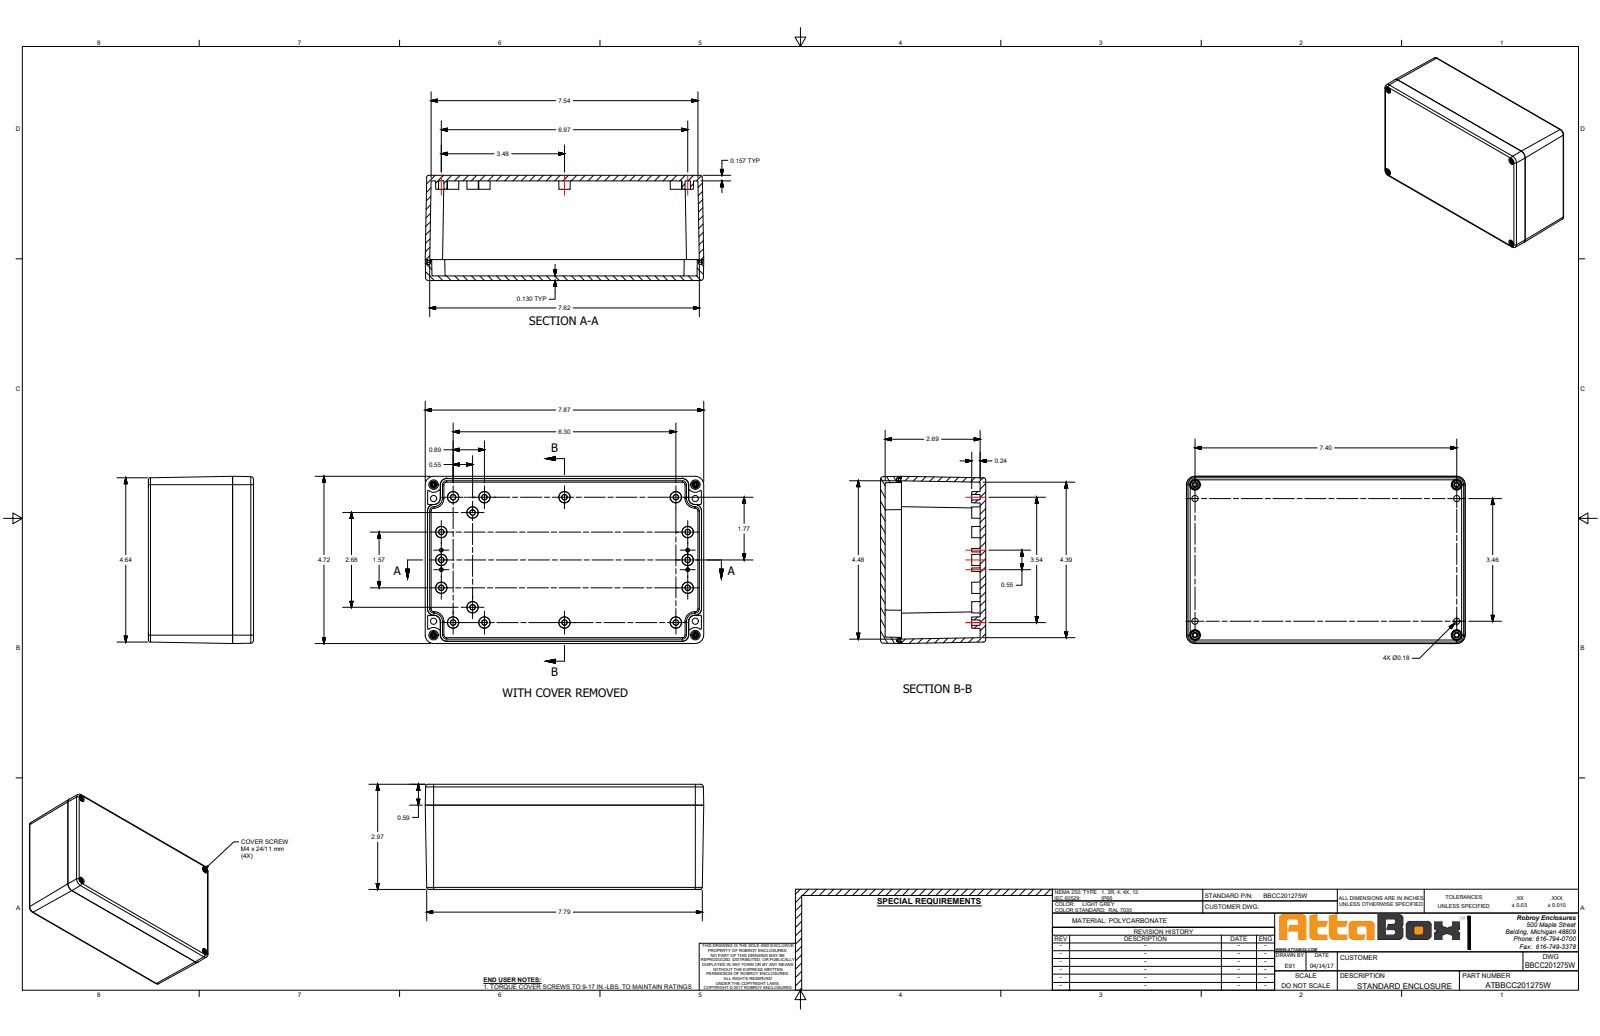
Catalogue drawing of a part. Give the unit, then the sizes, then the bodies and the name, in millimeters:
Units: millimetres
Overall size (bounding box): 200 × 120 × 75.5
Round holes (diameter × count): ⌀3.3 ×4, ⌀4.5 ×4, ⌀4.8 ×4, ⌀5 ×4, ⌀5.1 ×4, ⌀7 ×4, ⌀7.5 ×4, ⌀7.8 ×4
Round bosses / shafts (diameter × count): ⌀6.8 ×4, ⌀4.4 ×4, ⌀4 ×4, ⌀3.3 ×4
Partial cylindrical surfaces — rounded edges, fillets, slot ends (radius × count): R1 ×48, R0.5 ×38, R2.6 ×8, R5.2 ×8, R1.5 ×4, R2 ×4, R2.6 ×4, R3.1 ×4
Main face-to-face distances: 3.2, 75.5, 72.2, 3.3, 4, 68.2, 71.5, 120, 116.8, 115.6
Hole centre spacings: 10, 98, 188, 188.3, 212, 88, 108, 207.6
Volume: 332 800 mm³ · Surface area: 216 000 mm²
Bodies: 11 solids, 1691 faces (631 planar, 436 cylindrical, 624 other)
Part name (STEP PRODUCT): BBCC201275W
STEP written by: SolidWorks 2018 (AUTOMOTIVE_DESIGN)
